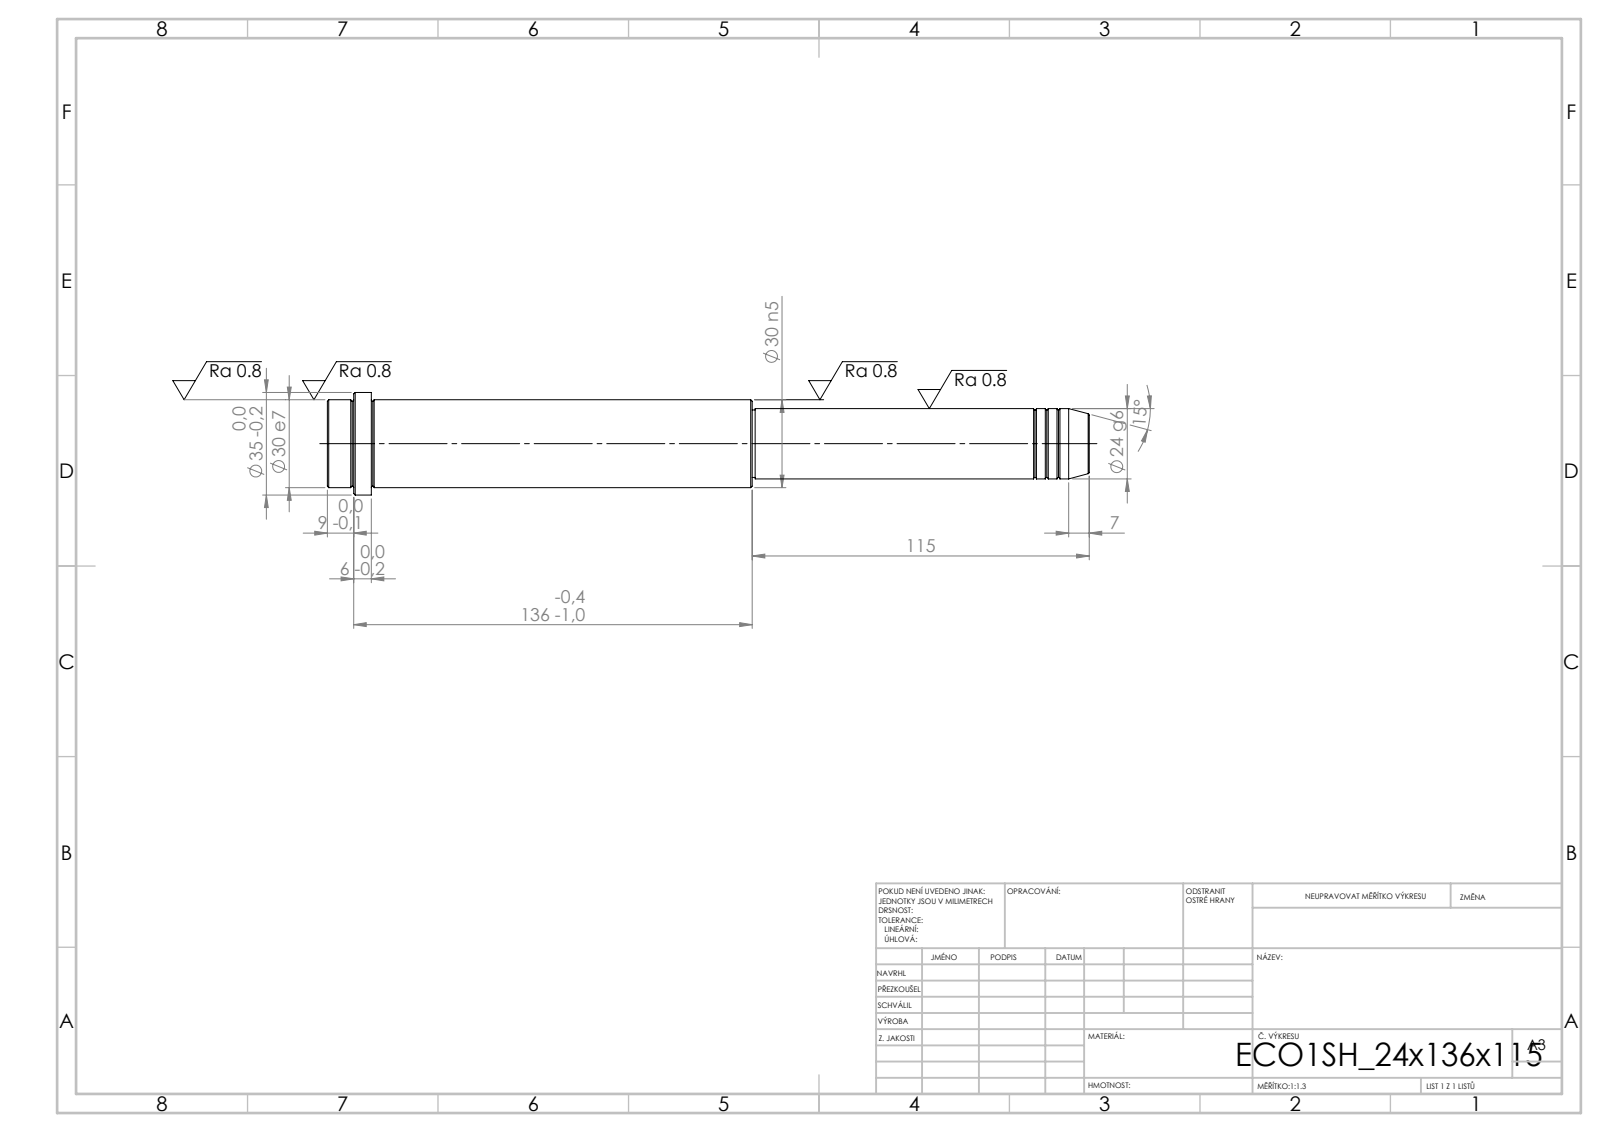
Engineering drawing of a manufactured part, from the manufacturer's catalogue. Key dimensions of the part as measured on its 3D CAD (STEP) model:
STEP written by: SolidWorks 2019 (CONFIG_CONTROL_DESIGN)
Units: millimetres
Bodies: 1 solid, 52 faces (6 planar, 16 cylindrical, 30 other)
Overall size (bounding box): 260 × 35 × 35
Volume: 155 346 mm³ · Surface area: 24 397 mm²
Round bosses / shafts (diameter × count): ⌀35 ×1, ⌀30 ×1, ⌀24 ×1, ⌀23 ×1
Main face-to-face distances: 260, 245, 15, 115, 130, 145, 251, 136, 6, 9
